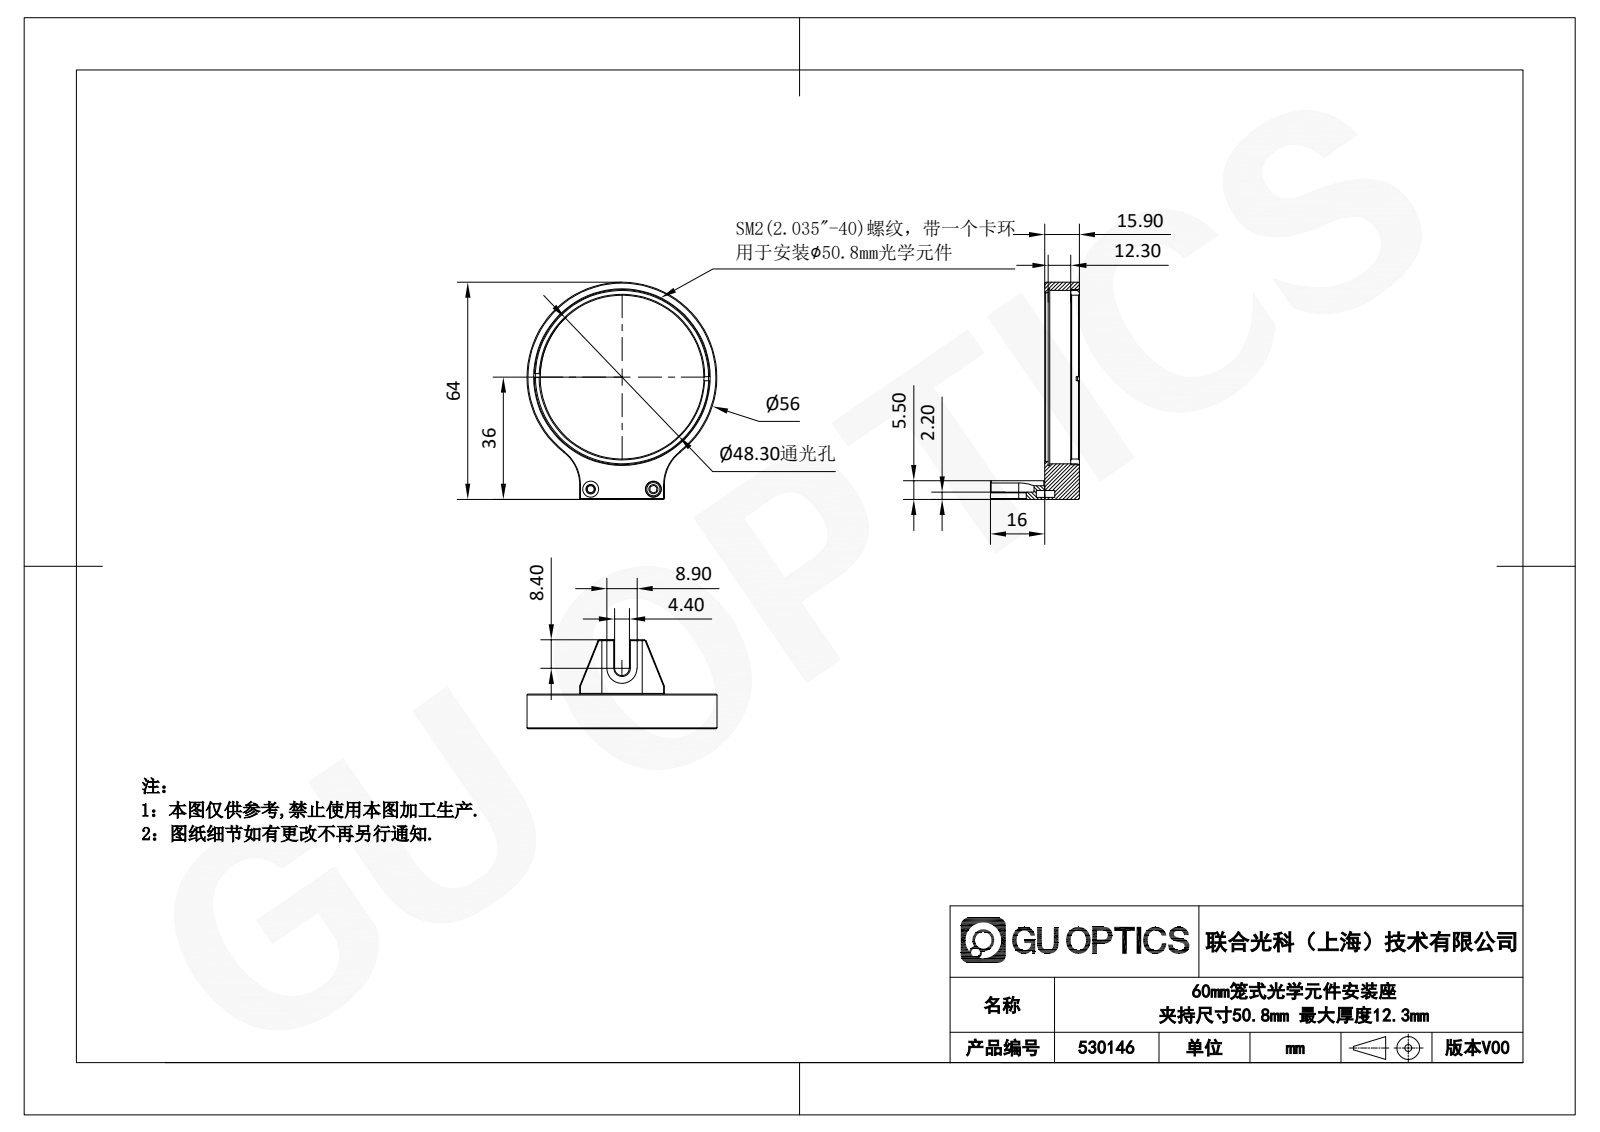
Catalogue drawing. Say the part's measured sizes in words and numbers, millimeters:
The part is named "530146". Its 3-D file was written by "SolidWorks 2020 (CONFIG_CONTROL_DESIGN)". It is 0 solids with 116 faces: 84 planar, 12 cylindrical and 20 other. Overall it measures 64 by 56 by 31.9 millimeters. Round holes: 2 of diameter 4.8, 1 of diameter 49.69, 1 of diameter 51.09, 1 of diameter 52.09. Round bosses or shafts: 1 of diameter 48.3. Partial cylindrical surfaces (rounded edges, fillets, slot ends): 2 of radius 12, 1 of radius 2.2, 1 of radius 4.45, 1 of radius 12.5, 1 of radius 28. The main face-to-face distances are 15.9, 1, 14.9, 13.4, 12.4, 2.5, 5.5, 0.5, 11.9, 1.5. The hole center spacings are 34.27, 18.5.
